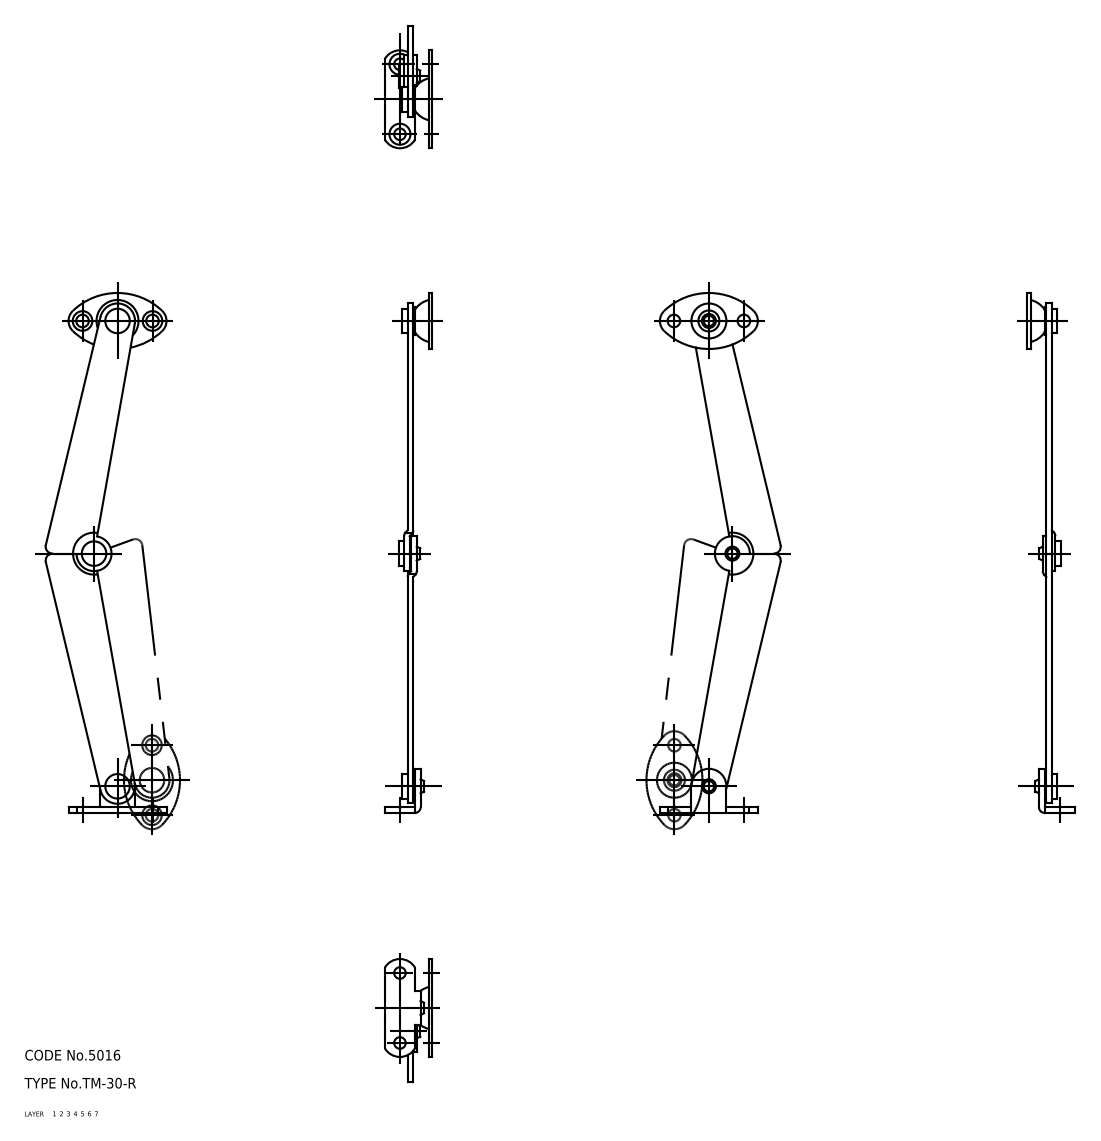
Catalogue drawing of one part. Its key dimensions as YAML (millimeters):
part_name: "rivet_3_mr; rivet_2_mr; rivet_1_mr; washer_mr-2 (+7 more)"
step_written_by: "CADfix (AUTOMOTIVE_DESIGN)"
units: millimeters
bodies: {solids: 10, faces: 130, planar: 0, cylindrical: 0, other: 130}
overall_size: [148.6, 34.54, 13.6]
volume: 4080
surface_area: 6693
